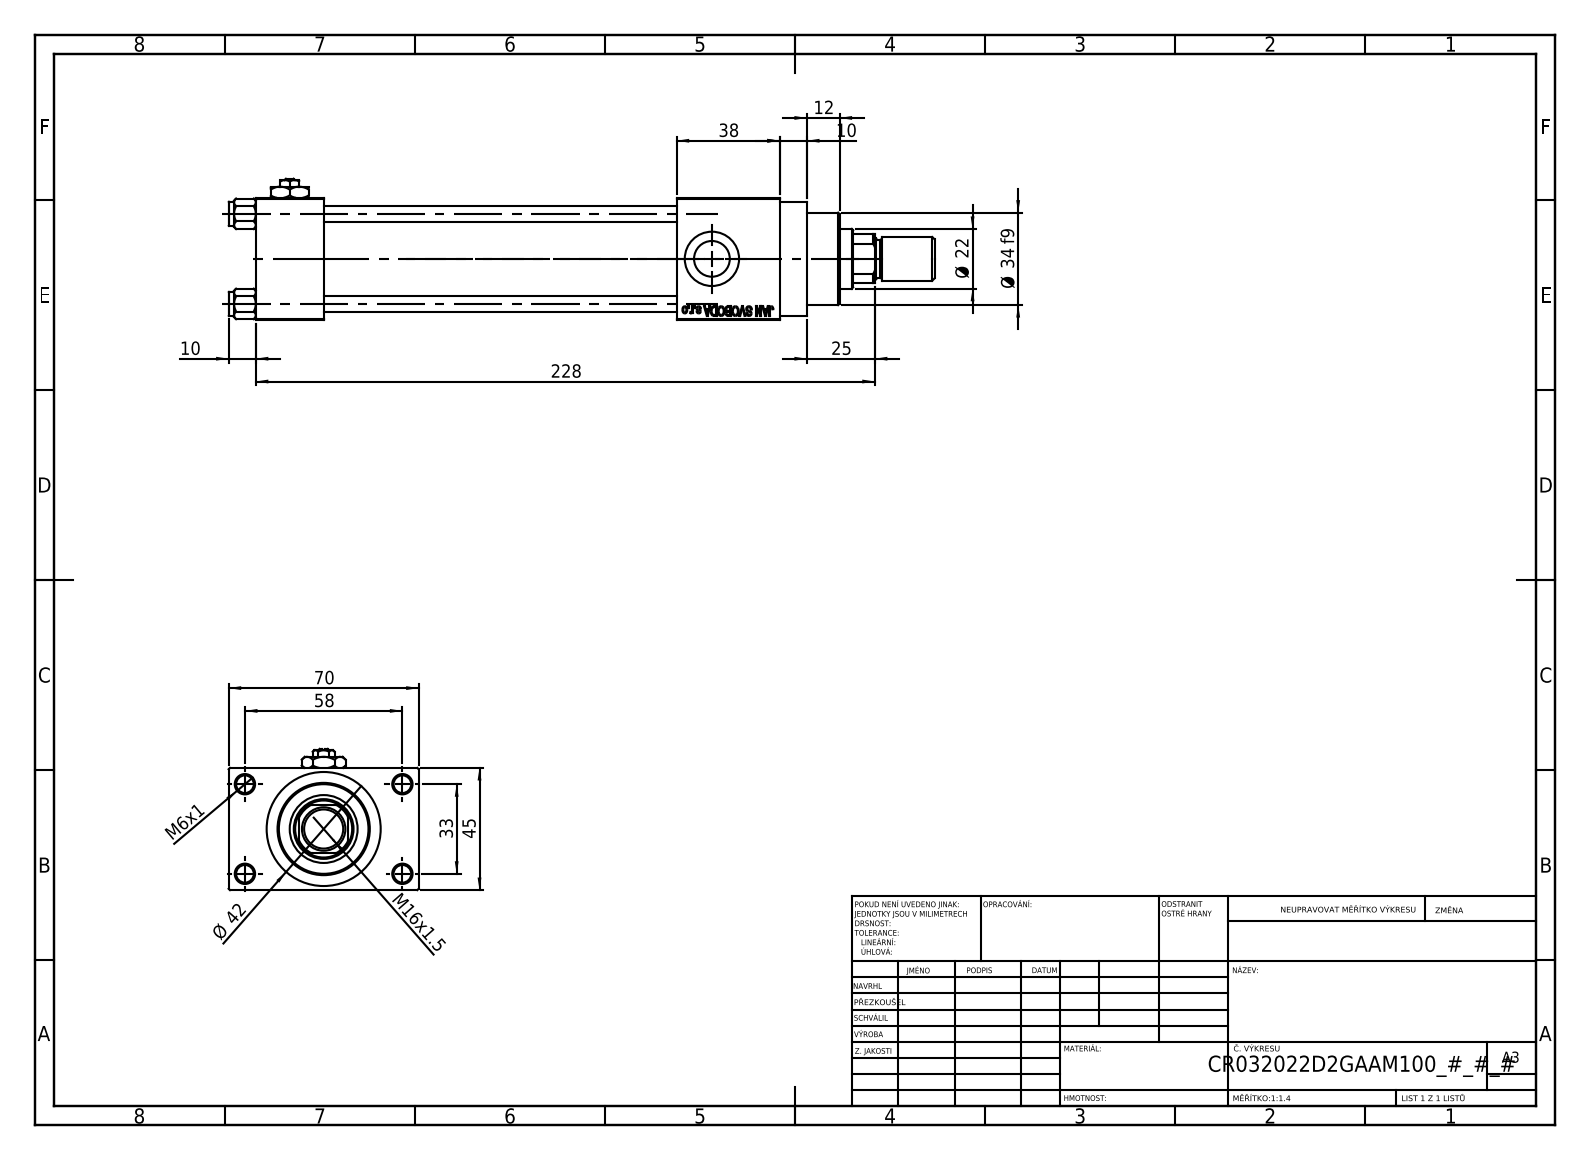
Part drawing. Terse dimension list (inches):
name: Zatka_pro_OIL_PORT; ROD_END_AH; V215_VC_A; V215CR_VCP_D (+3 more)
written by: SolidWorks 2019 (CONFIG_CONTROL_DESIGN)
unit: in
bodies: 13 solids, 1159 faces (522 planar, 93 cylindrical, 544 other)
size: 10.236 × 2.756 × 2.047
volume: 19.15 in³; area: 172.5 in²
holes: 4× ⌀0.236, 4× ⌀0.256, 2× ⌀0.276, 2× ⌀0.518, 2× ⌀0.787, 1× ⌀0.413, 1× ⌀0.866, 1× ⌀0.945, 1× ⌀0.984, 1× ⌀1.26, 1× ⌀1.299
bosses: 4× ⌀0.354, 1× ⌀1.654, 1× ⌀1.496, 1× ⌀1.339, 1× ⌀0.63, 1× ⌀0.551
rounds: 1× R0.413
face distances: 1.772, 0.984, 0.492, 2.264, 5.118, 6.102, 6.614, 1.496, 7.598, 2.756
hole spacings: 0.488, 0.924, 1.307, 1.314, 1.392, 1.795, 2.219, 1.299
